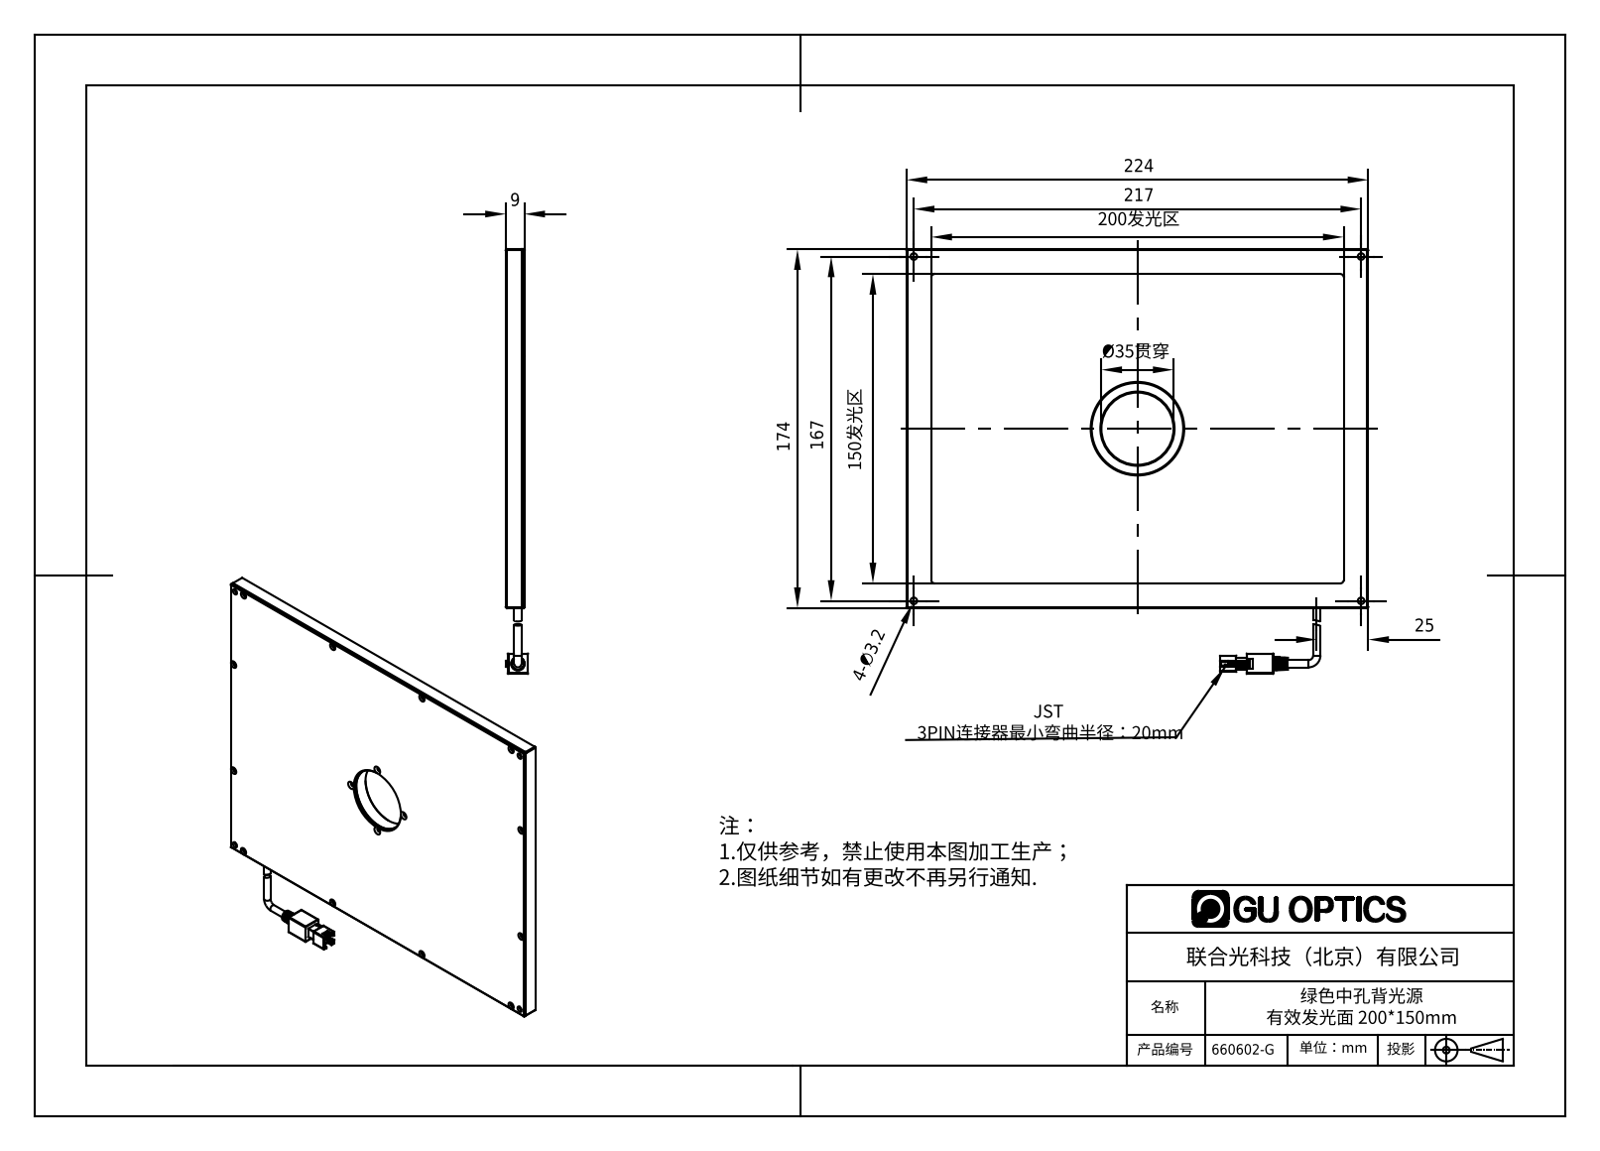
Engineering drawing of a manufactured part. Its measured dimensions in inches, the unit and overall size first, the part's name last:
Units: inches
Overall size (bounding box): 8.819 × 8.11 × 0.427
Round holes (diameter × count): ⌀0.063 ×16, ⌀0.094 ×12, ⌀0.087 ×4, ⌀0.126 ×4, ⌀1.378 ×1, ⌀1.701 ×1
Round bosses / shafts (diameter × count): ⌀0.138 ×2, ⌀1.787 ×1, ⌀1.693 ×1
Partial cylindrical surfaces — rounded edges, fillets, slot ends (radius × count): R0.004 ×15, R0.008 ×13, R0.016 ×12, R0.059 ×6, R0.079 ×4, R0.157 ×4, R0.012 ×1, R0.027 ×1
Main face-to-face distances: 0.157, 0.059, 0.256, 0.315, 0.098, 0.039, 0.197, 0.295, 0.354, 0.217
Hole centre spacings: 2.677, 7.172, 0.259, 0.787, 1.113, 1.91, 1.971, 2.87
Volume: 13.24 in³ · Surface area: 287.4 in²
Bodies: 10 solids, 1145 faces (820 planar, 168 cylindrical, 157 other)
Part name (STEP PRODUCT): 660602-G
STEP written by: SolidWorks 2016 (AUTOMOTIVE_DESIGN)
